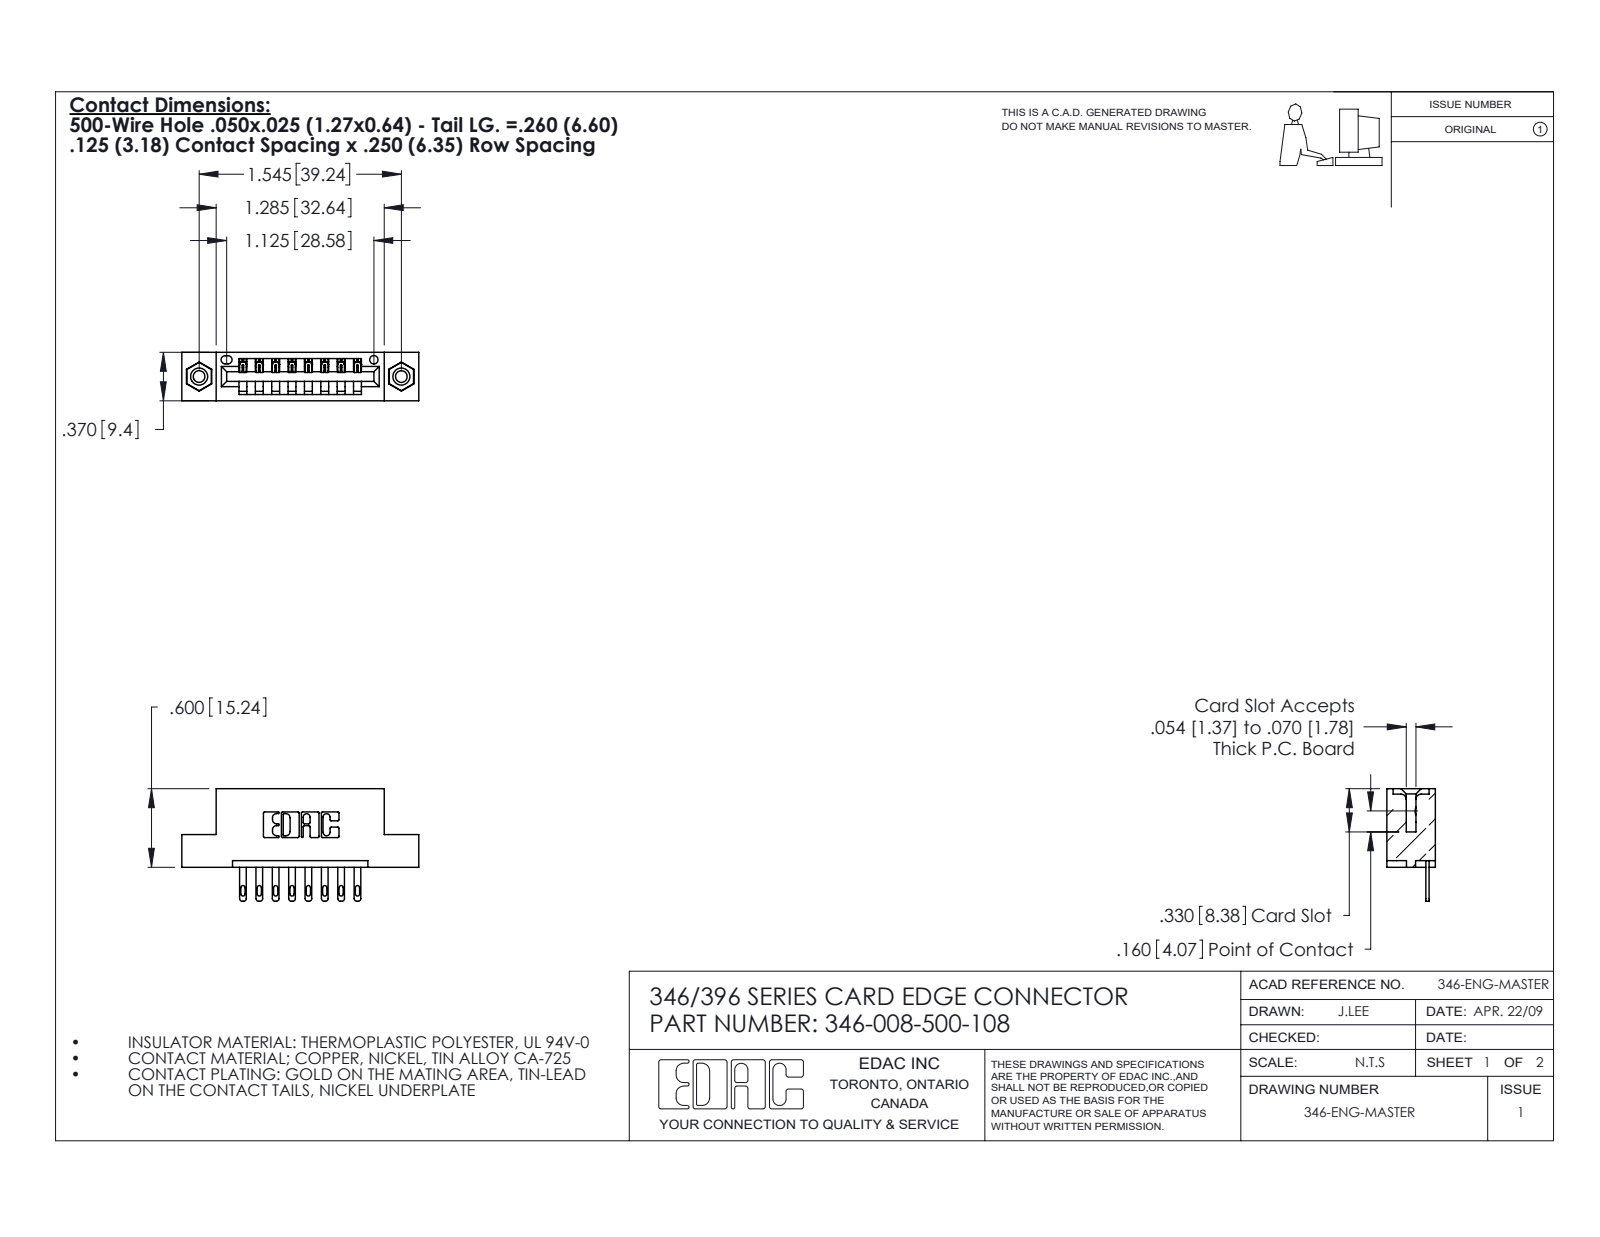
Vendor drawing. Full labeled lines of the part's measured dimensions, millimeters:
Part name (STEP PRODUCT): 345-292-001_345-293-100; 346 Part_Flush Mounting Lugs - 0.156 Dia-TI; 345-250-001_345-250-003-102; 346-008-500-108
STEP written by: SolidWorks 2020 (CONFIG_CONTROL_DESIGN)
Units: millimetres
Bodies: 11 solids, 614 faces (380 planar, 218 cylindrical, 16 other)
Overall size (bounding box): 46 × 21.8 × 9.4
Volume: 4 160 mm³ · Surface area: 4 879 mm²
Round holes (diameter × count): ⌀2.3 ×2, ⌀3.2 ×2, ⌀4 ×2, ⌀1.6 ×1
Round bosses / shafts (diameter × count): ⌀3.9 ×2
Partial cylindrical surfaces — rounded edges, fillets, slot ends (radius × count): R0.3 ×22, R0.2 ×16, R0.4 ×16, R0.5 ×16, R0.2 ×6, R0.8 ×6, R0.7 ×3, R0.8 ×2
Main face-to-face distances: 6.4, 9.4, 1.2, 8.2, 12.7, 1.8, 7.6, 0.6, 3.8, 5.6
Hole centre spacings: 6.2, 34.1, 39.2
